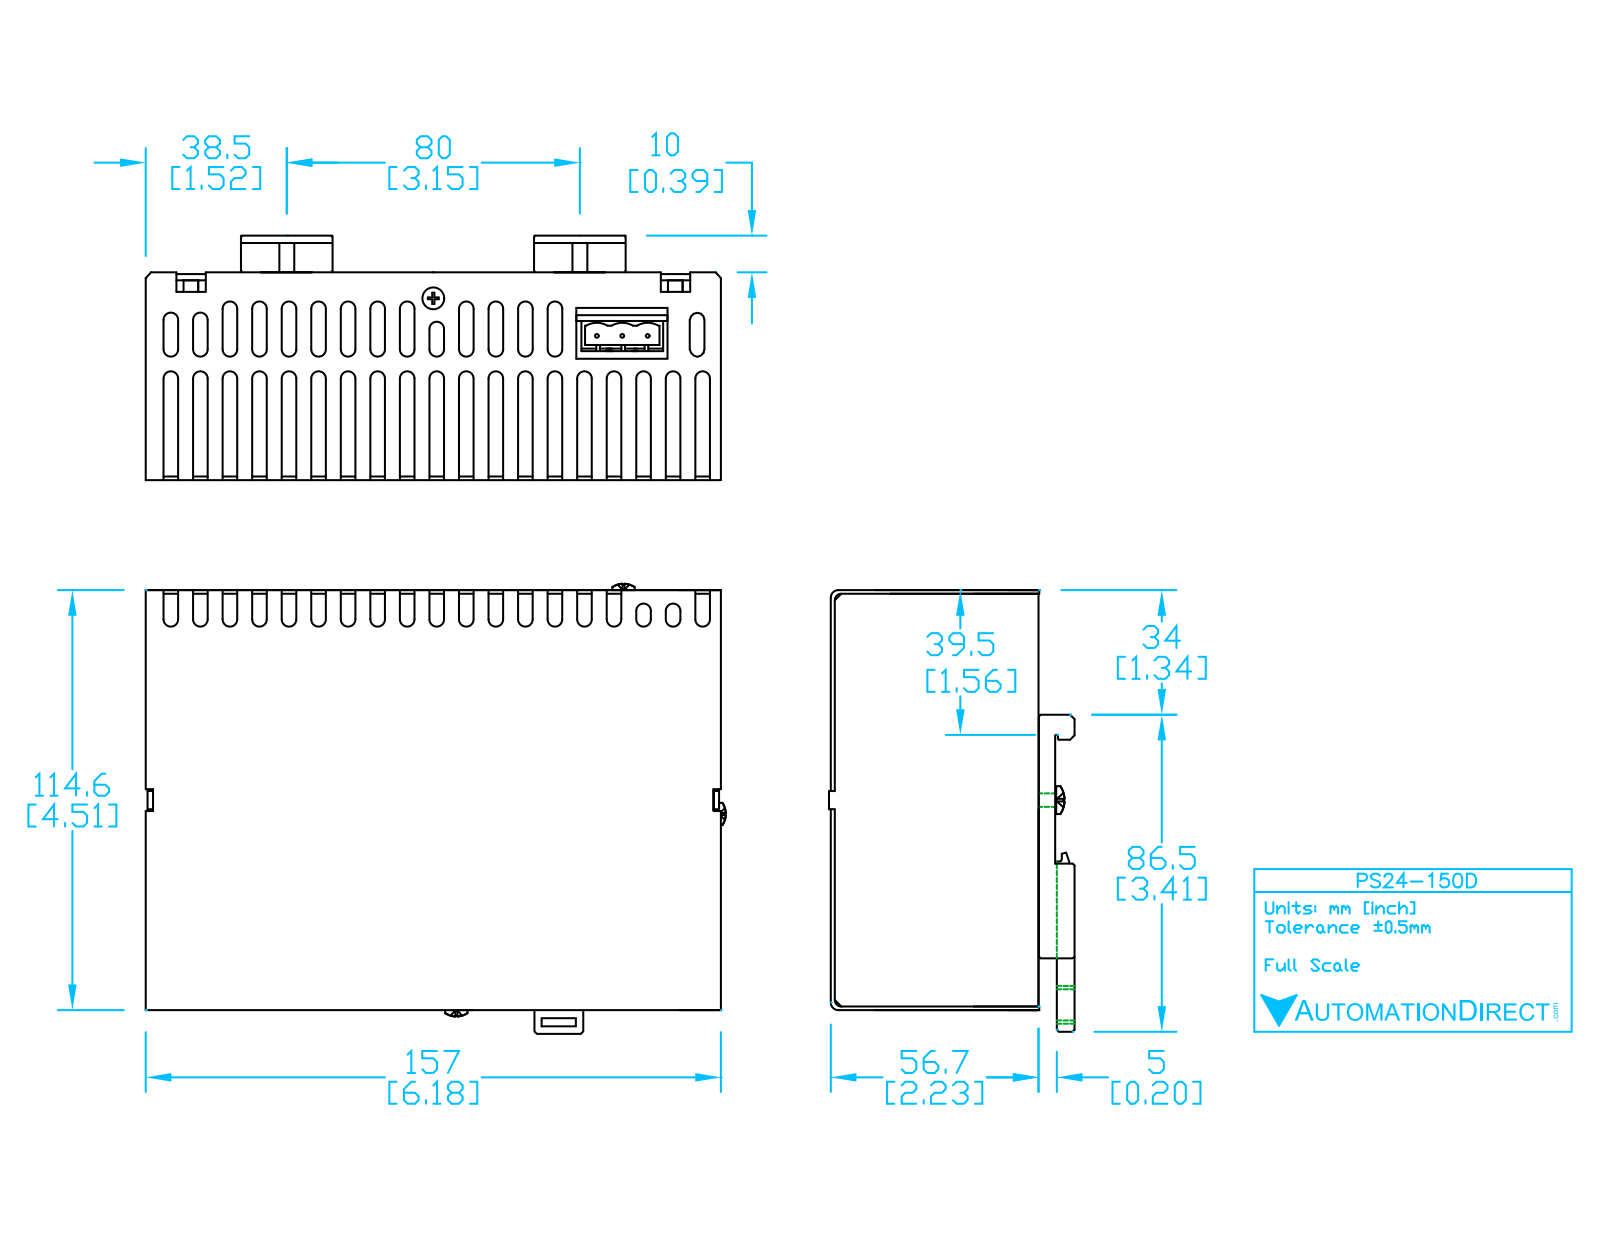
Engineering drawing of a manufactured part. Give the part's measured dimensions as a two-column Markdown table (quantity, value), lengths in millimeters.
| quantity | value |
| --- | --- |
| part name | PS24-150D |
| STEP written by | SolidWorks 2011 (CONFIG_CONTROL_DESIGN) |
| units | millimeters |
| bodies | 1 solid, 998 faces (618 planar, 302 cylindrical, 78 other) |
| overall size | 159.4 × 135.2 × 68.4 |
| volume | 640 100 mm³ |
| surface area | 119 000 mm² |
| round holes (diameter × count) | 3.8 × 5 |
| round bosses / shafts (diameter × count) | 6.7 × 2, 5.3 × 2, 7.6 × 1, 5.4 × 1 |
| partial cylindrical surfaces (radius × count) | 1.9 × 97, 1.5 × 4, 0.4 × 2, 0.5 × 2, 1.3 × 2, 2.5 × 2 |
| main face-to-face distances | 1, 113.5, 63.4, 56.6, 56.6, 55.6, 1, 157.2, 88.9, 25.5 |
| hole center spacings | 7.6, 5.1, 15.2, 160.4, 163.7, 165.4, 168.8, 170.5 |
